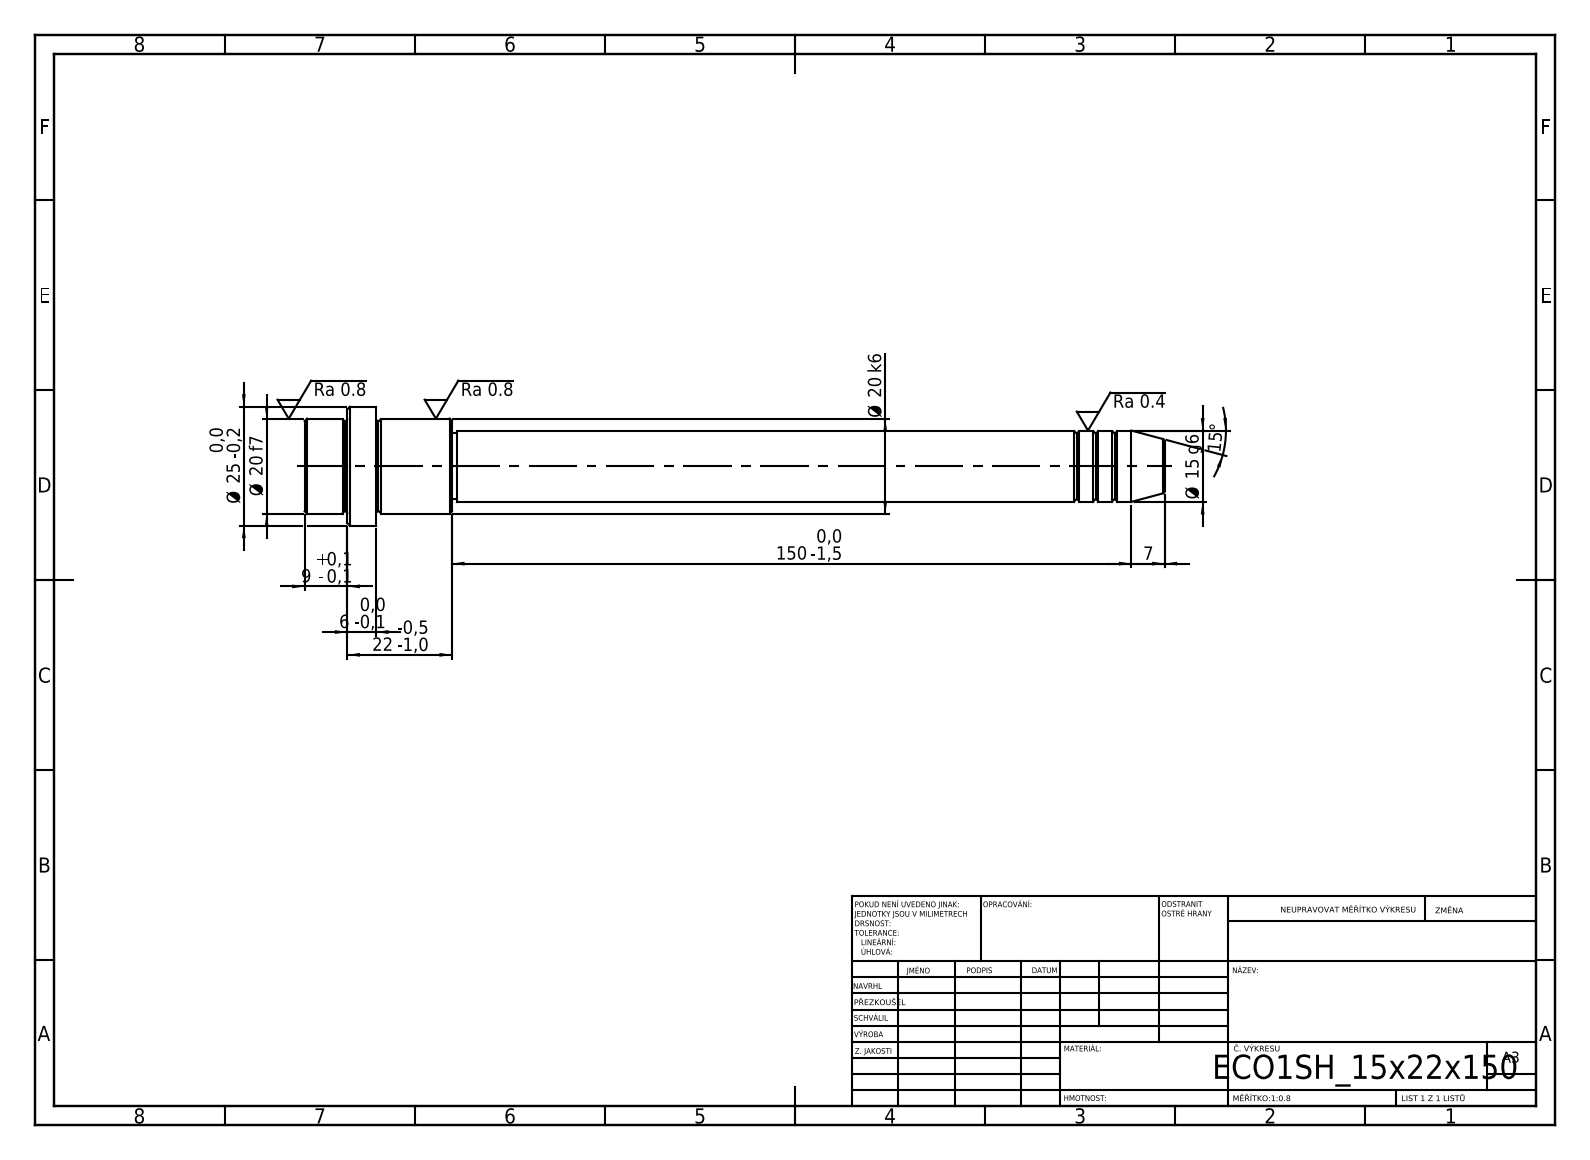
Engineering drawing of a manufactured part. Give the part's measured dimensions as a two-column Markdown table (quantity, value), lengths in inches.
| quantity | value |
| --- | --- |
| STEP written by | SolidWorks 2019 (CONFIG_CONTROL_DESIGN) |
| units | inches |
| bodies | 1 solid, 52 faces (6 planar, 16 cylindrical, 30 other) |
| overall size | 7.126 × 0.984 × 0.984 |
| volume | 2.25 in³ |
| surface area | 15.65 in² |
| round bosses / shafts (diameter × count) | 0.984 × 1, 0.787 × 1, 0.591 × 1, 0.551 × 1 |
| main face-to-face distances | 0.591, 0.236, 0.354, 0.63, 0.866, 1.22, 5.906, 6.535, 6.772, 7.126 |
